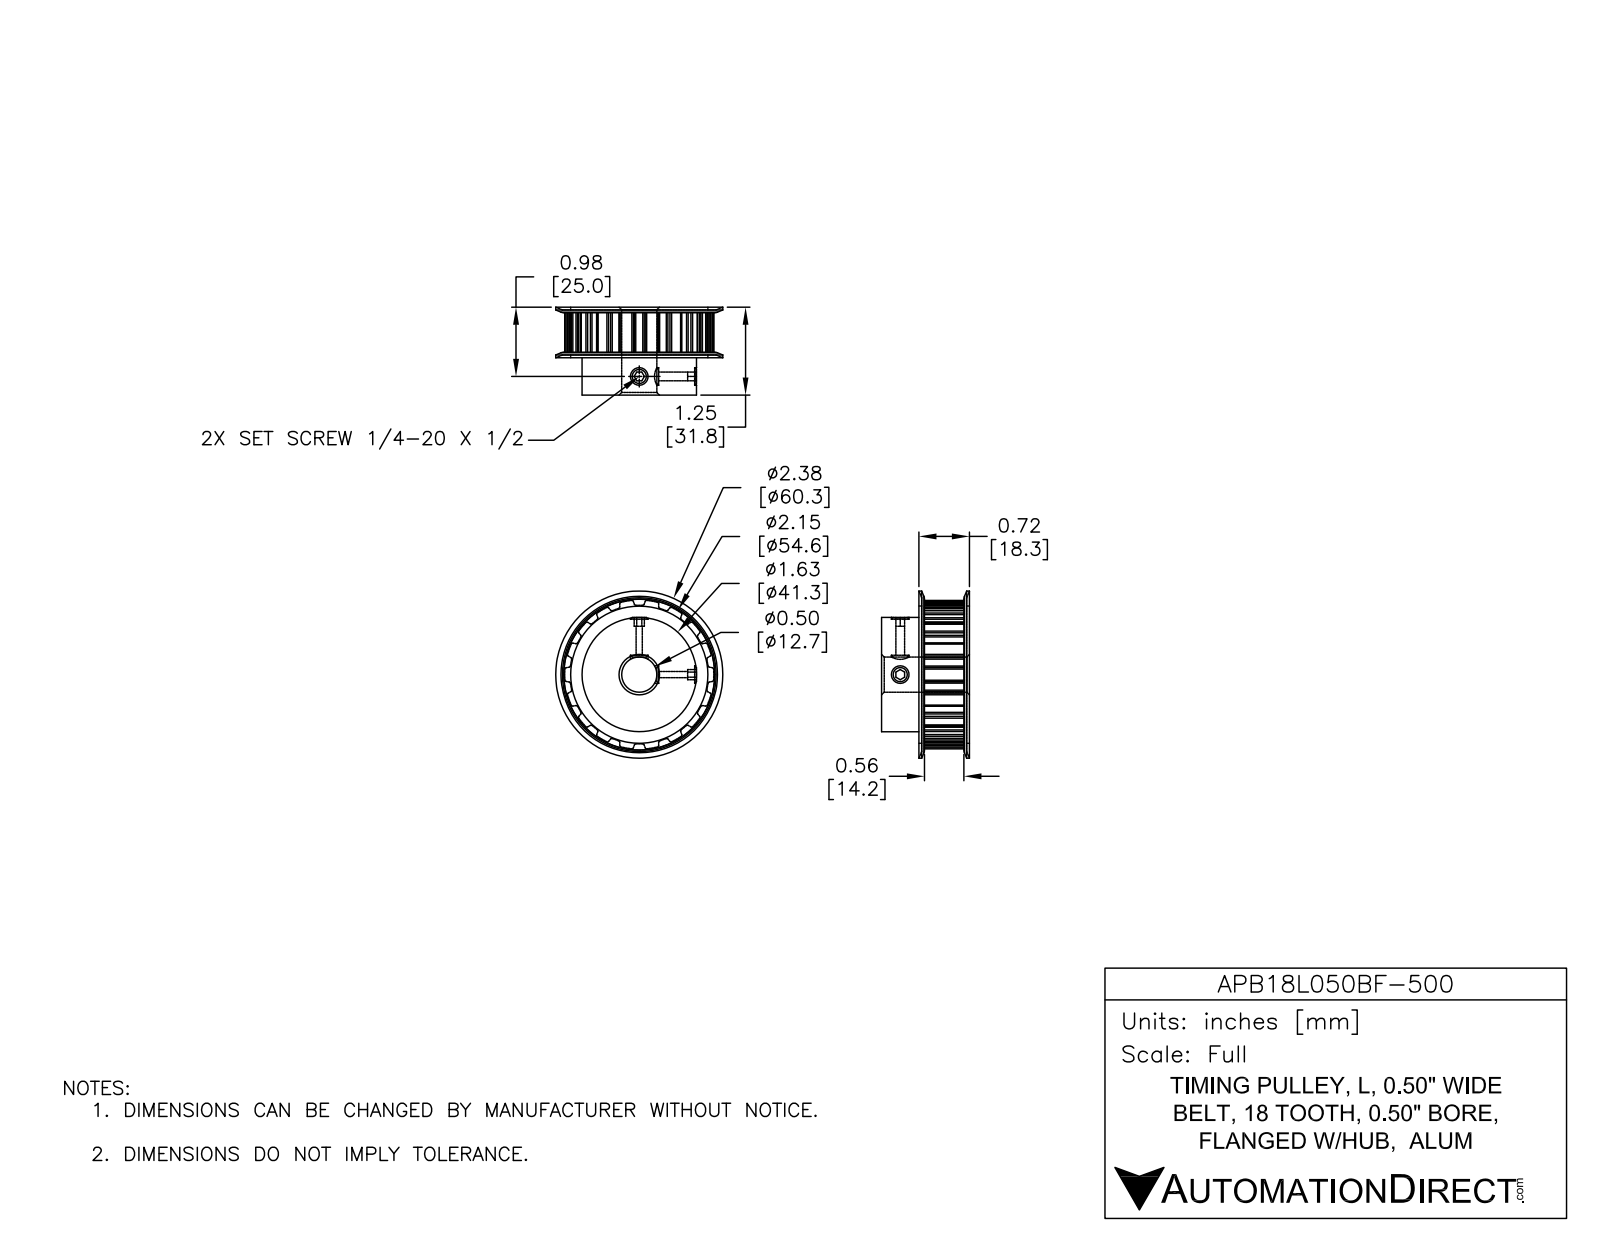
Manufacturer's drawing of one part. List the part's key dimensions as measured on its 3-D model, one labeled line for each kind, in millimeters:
Part name (STEP PRODUCT): APB18L050BF-500
STEP written by: SolidWorks 2014 (AUTOMOTIVE_DESIGN)
Units: millimetres
Bodies: 1 solid, 152 faces (60 planar, 70 cylindrical, 22 other)
Overall size (bounding box): 60.3 × 60.3 × 31.8
Volume: 54 190 mm³ · Surface area: 13 340 mm²
Round holes (diameter × count): ⌀2.2 ×2, ⌀12.7 ×1
Round bosses / shafts (diameter × count): ⌀41.3 ×1
Partial cylindrical surfaces — rounded edges, fillets, slot ends (radius × count): R0.4 ×36, R25.5 ×1
Main face-to-face distances: 31.8, 17.3, 14.5, 1, 16.3, 30.7, 53.8, 53.8, 1, 15.2
